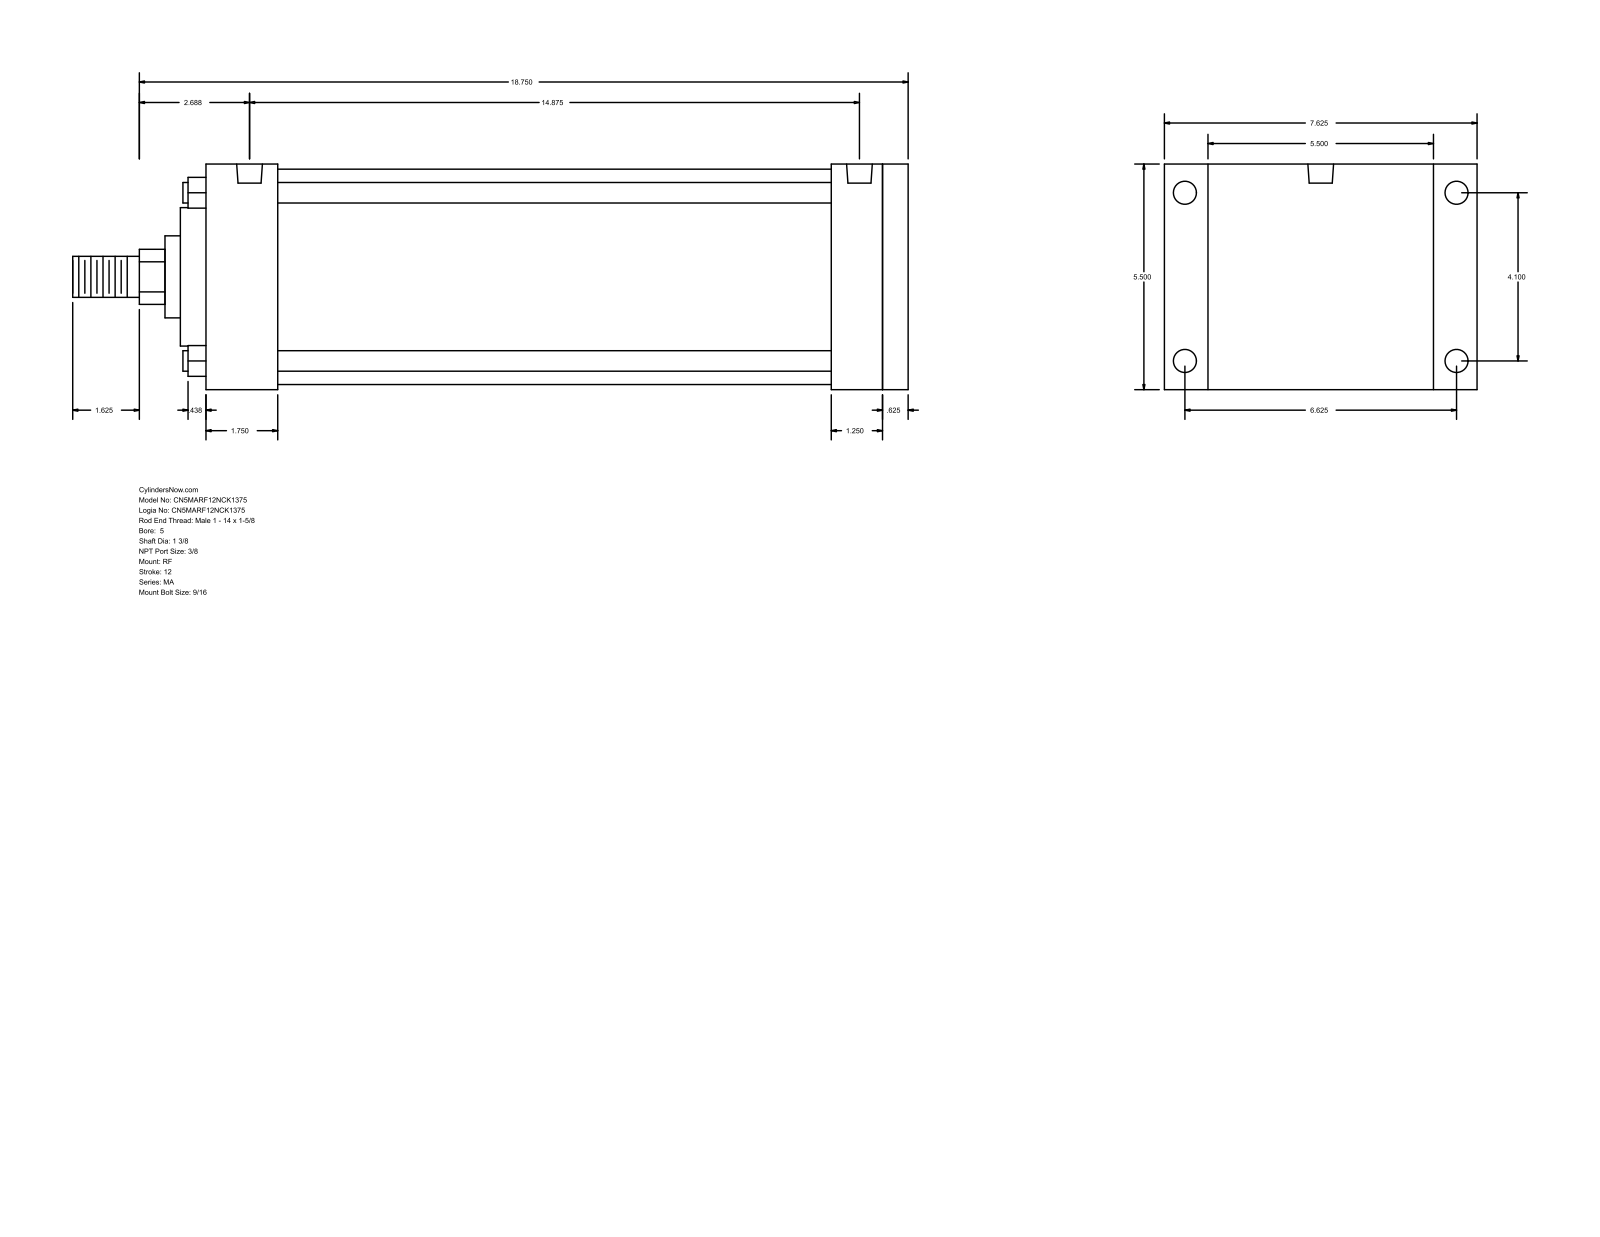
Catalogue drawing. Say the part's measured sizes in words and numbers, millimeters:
The part is named "MA_RF__0500_1.375". Its 3-D file was written by "GSSL Pune (CONFIG_CONTROL_DESIGN)". It is 0 solids with 94 faces: 65 planar, 29 cylindrical and 0 other. Overall it measures 517.52 by 193.68 by 139.7 millimeters. Round holes: 4 of diameter 11.11, 4 of diameter 14.29, 2 of diameter 15.93. Round bosses or shafts: 4 of diameter 12.7, 1 of diameter 133.35, 1 of diameter 85.72, 1 of diameter 50.8, 1 of diameter 34.92, 1 of diameter 25.4. Partial cylindrical surfaces (rounded edges, fillets, slot ends): 1 of radius 17.06. The main face-to-face distances are 139.7, 434.98, 15.87, 419.11, 44.45, 374.66, 390.53, 387.35, 342.9, 31.76. The hole center spacings are 4.77, 104.14, 168.28, 197.9, 368.29, 373.06, 377.83.
